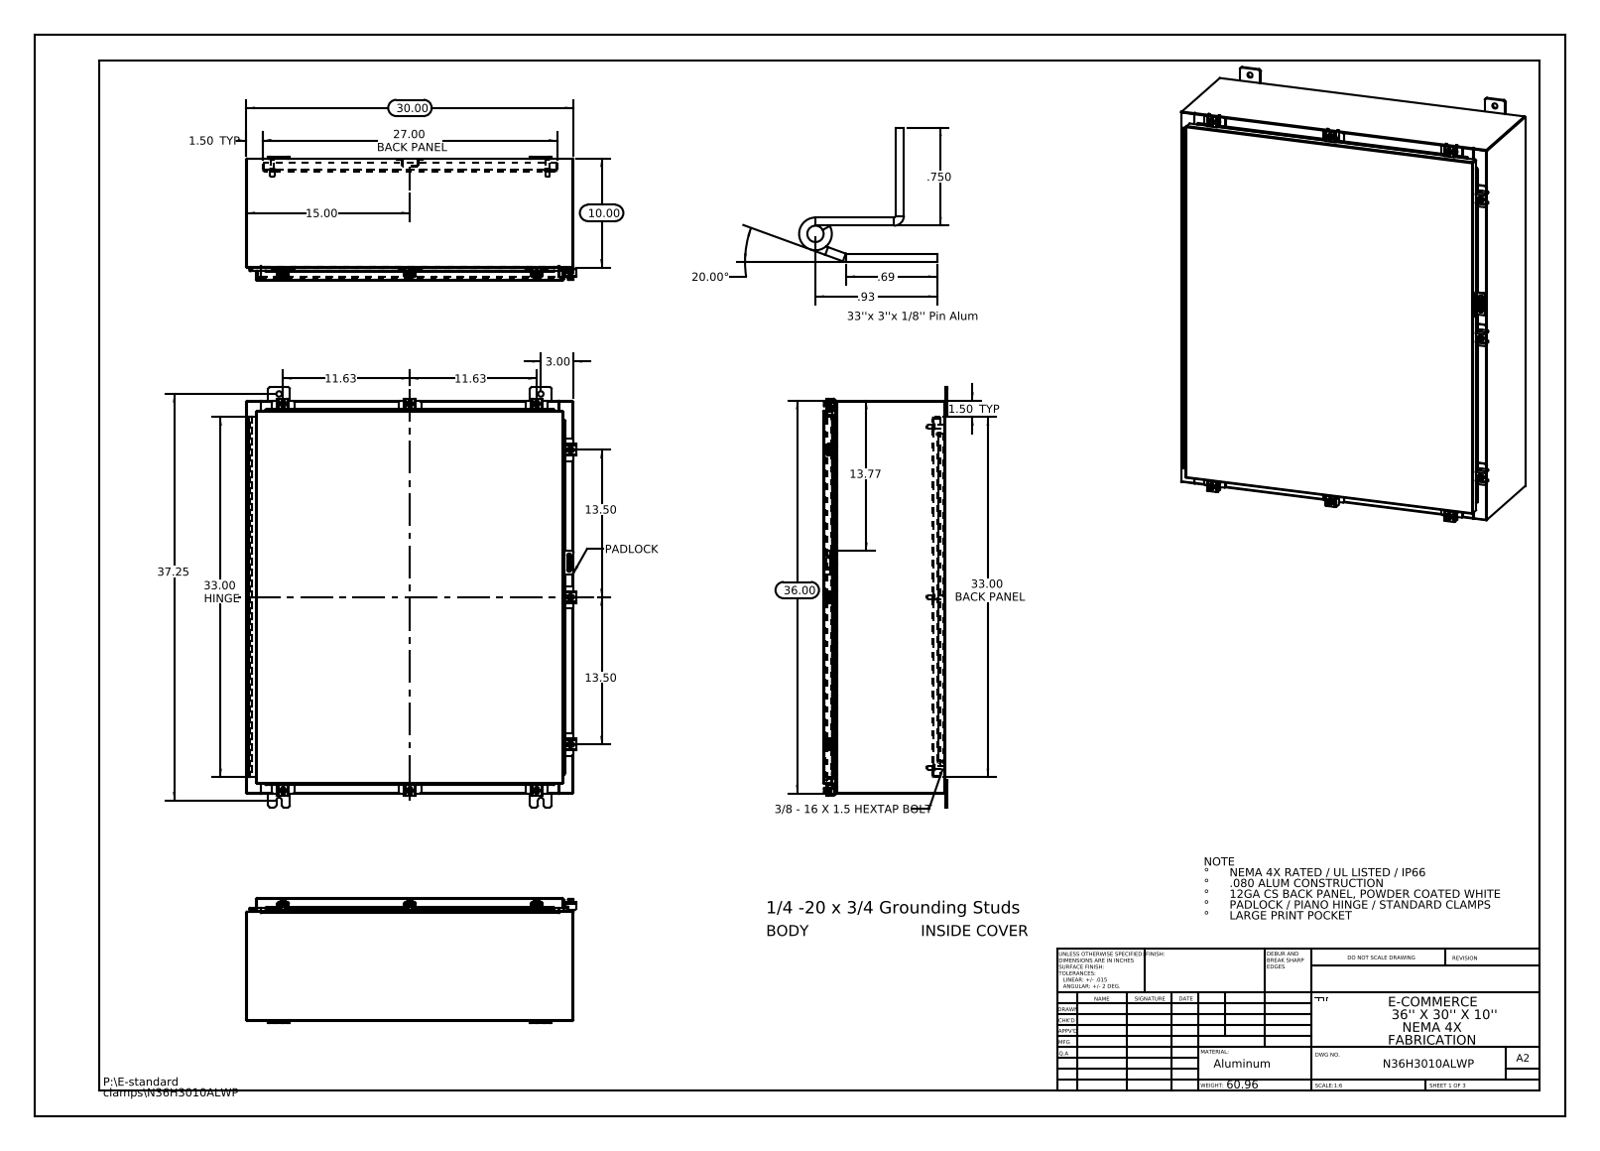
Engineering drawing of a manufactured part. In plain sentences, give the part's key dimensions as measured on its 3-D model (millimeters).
The part is named "N36H3010ALWP Backpanel; N36H3010ALWP Bottom; N36H3010ALWP 22104005_DEFAULT; N36H3010ALWP Hinge Enclosure Side2 (+8 more)". Its 3-D file was written by "SolidWorks 2013 (CONFIG_CONTROL_DESIGN)". It is 65 solids with 2456 faces: 1288 planar, 1028 cylindrical and 140 other. Overall it measures 977.9 by 767.4 by 289.3 millimeters. Its volume is 6 589 000 cubic millimeters and its surface area 6 481 000 square millimeters. Round holes: 10 of diameter 12.7, 9 of diameter 5.4, 9 of diameter 6.6, 2 of diameter 3.2, 1 of diameter 3.2. Round bosses or shafts: 10 of diameter 6.4, 9 of diameter 12.7, 9 of diameter 10.1, 6 of diameter 15.9, 6 of diameter 9.5, 6 of diameter 8.4. Partial cylindrical surfaces (rounded edges, fillets, slot ends): 42 of radius 1.5, 31 of radius 0.3, 25 of radius 2.2, 24 of radius 4.8, 18 of radius 3, 18 of radius 3.6, 13 of radius 1.3, 12 of radius 2. The main face-to-face distances are 1.9, 282.6, 280.7, 284.5, 2.6, 25.4, 257.2, 27.3, 255.3, 29.9. The hole center spacings are 396.9, 451, 754.2, 847.5, 947.6, 641.4, 900.5, 47.2.
